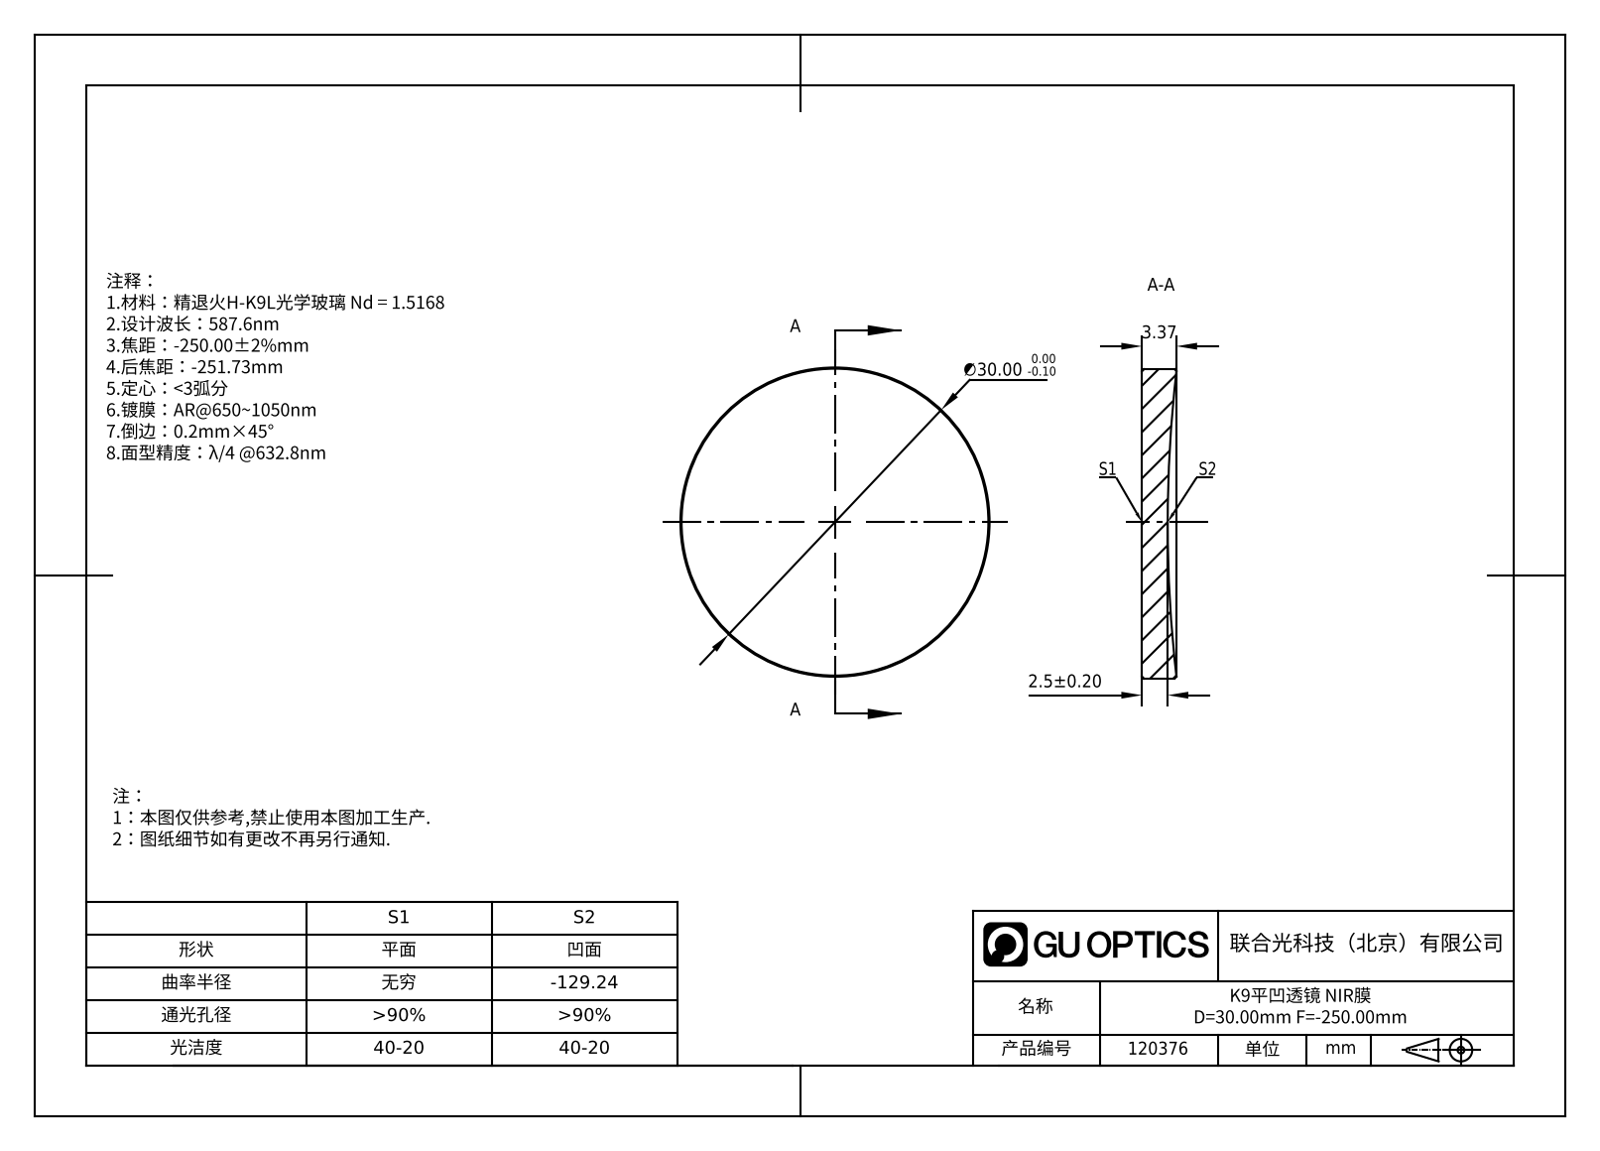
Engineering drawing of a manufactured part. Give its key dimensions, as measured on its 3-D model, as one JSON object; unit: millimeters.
{"part_name": "GL13-030-250", "step_written_by": "SolidWorks 2022 (AUTOMOTIVE_DESIGN)", "units": "millimeters", "bodies": {"solids": 1, "faces": 9, "planar": 1, "cylindrical": 2, "other": 6}, "overall_size": [30, 30, 3.35], "volume_mm3": 2070, "surface_area_mm2": 1711, "round_bosses_or_shafts": [[30, 1]]}
